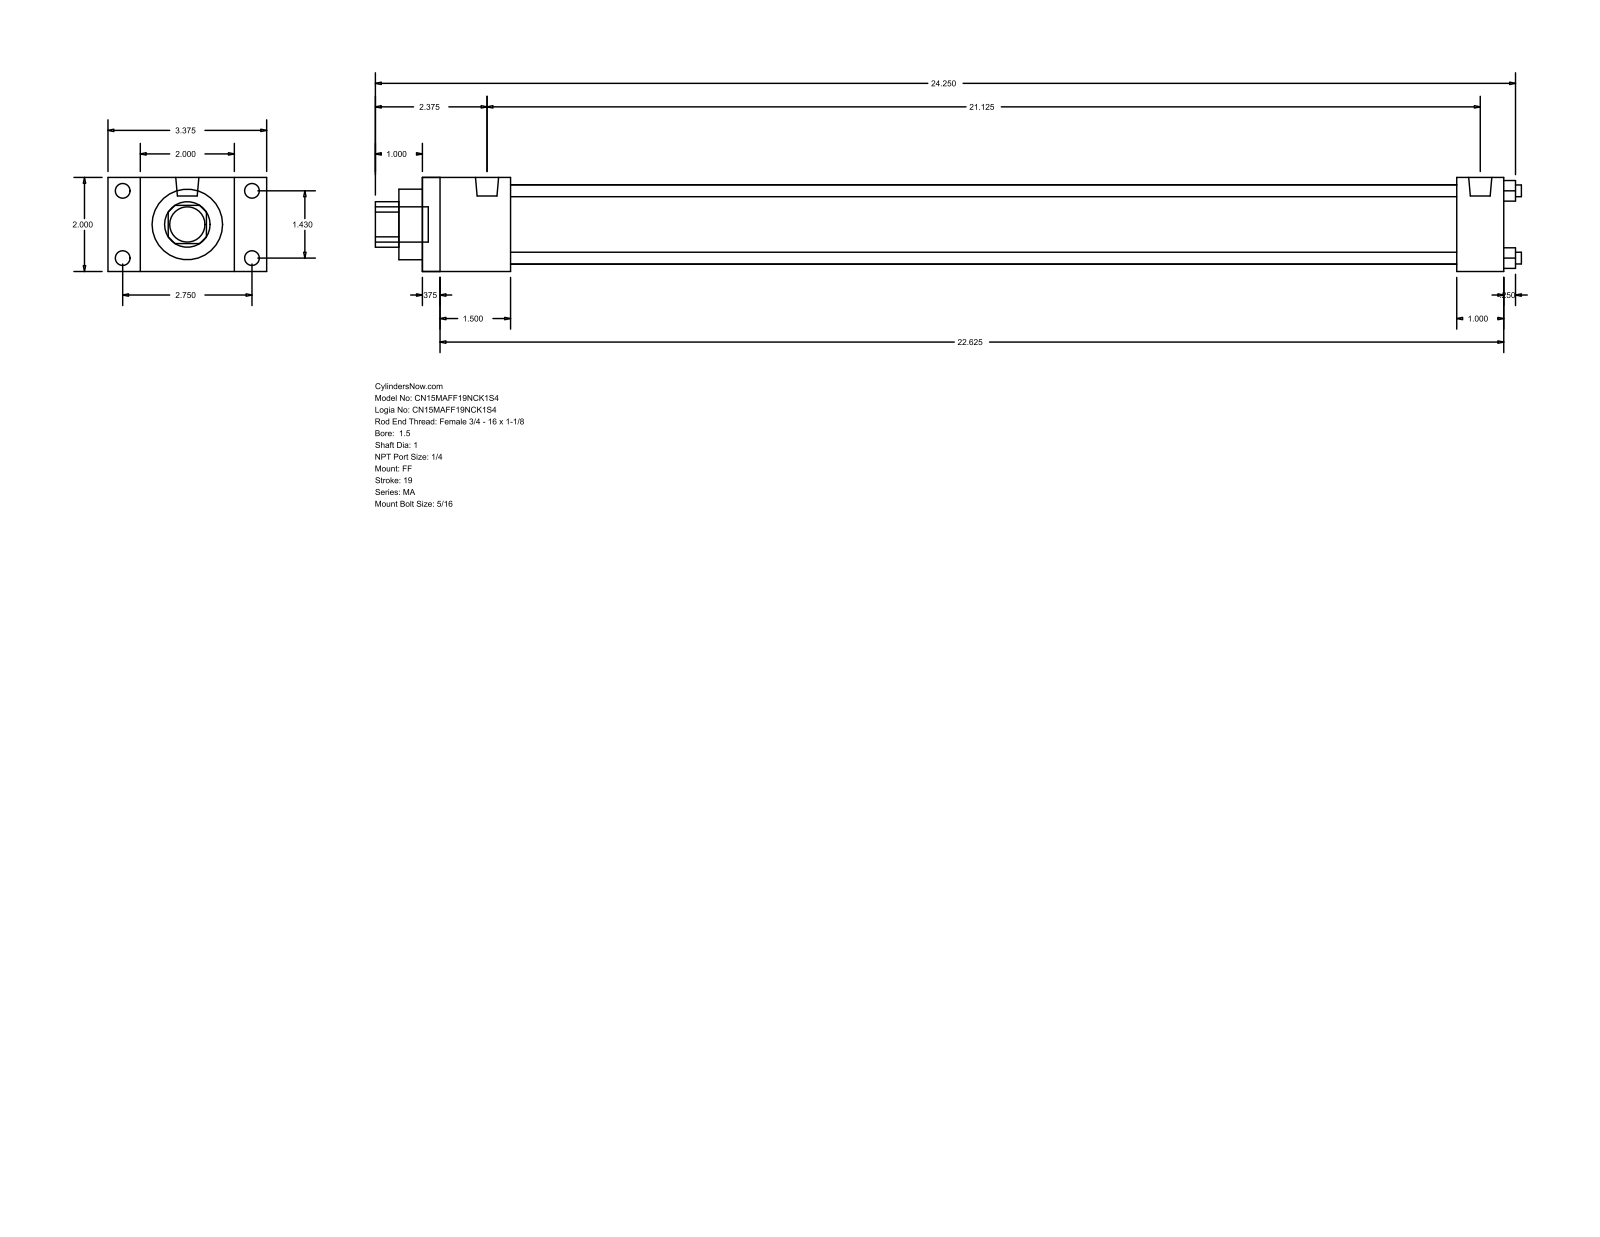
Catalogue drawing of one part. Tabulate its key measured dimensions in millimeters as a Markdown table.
| quantity | value |
| --- | --- |
| part name | MA_FF__0150_1 |
| STEP written by | GSSL Pune (CONFIG_CONTROL_DESIGN) |
| units | millimeters |
| bodies | 0 solids, 92 faces (64 planar, 28 cylindrical, 0 other) |
| overall size | 619.12 × 85.72 × 50.8 |
| round holes (diameter × count) | 6.35 × 4, 25.4 × 1, 38.1 × 1, 42.93 × 1 |
| round bosses / shafts (diameter × count) | 7.94 × 8, 12.49 × 2, 19.05 × 1 |
| partial cylindrical surfaces (radius × count) | 12.29 × 1 |
| main face-to-face distances | 50.8, 584.2, 9.52, 574.68, 25.4, 47.63, 558.8, 38.11, 549.28, 511.17 |
| hole center spacings | 25.68, 36.32, 51.36 |
